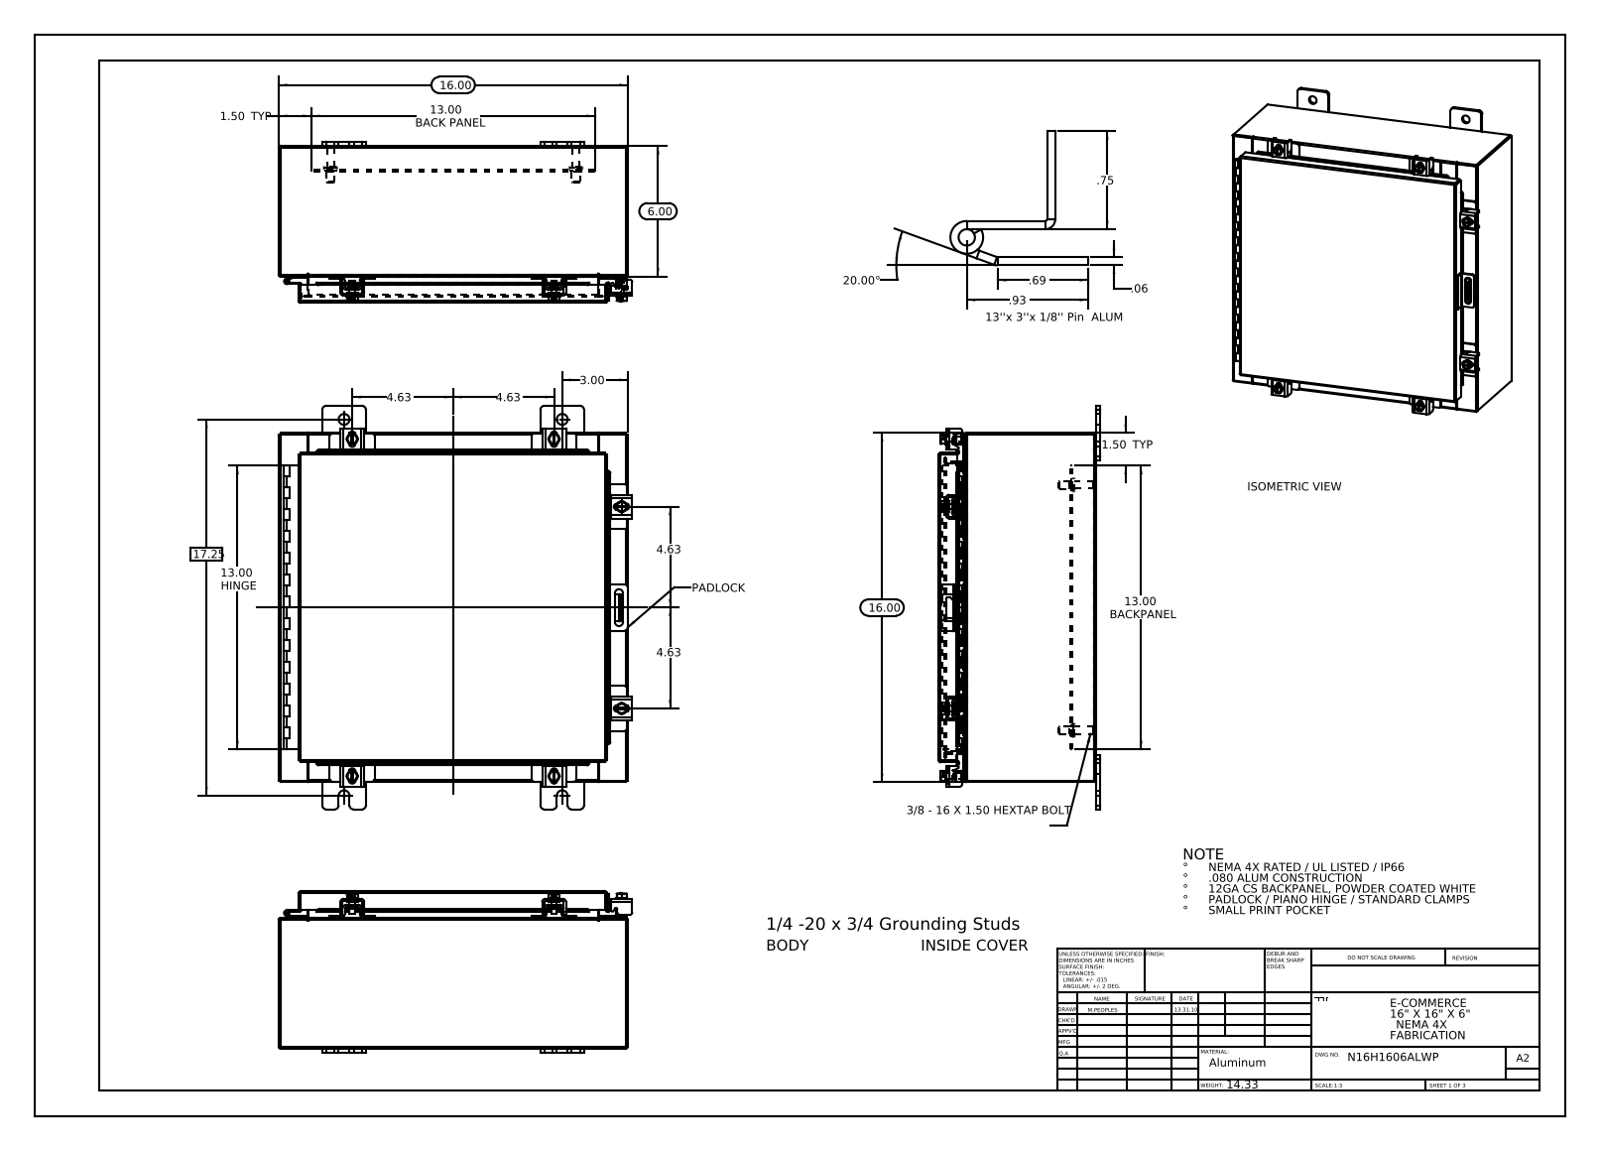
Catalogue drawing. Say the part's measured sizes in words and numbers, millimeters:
The part is named "N16H1606ALWP Backpanel; N16H1606ALWP; N16H1606ALWP 22104005_DEFAULT; N16H1606ALWP Mounting Studs (+8 more)". Its 3-D file was written by "SolidWorks 2013 (CONFIG_CONTROL_DESIGN)". It is 47 solids with 1501 faces: 800 planar, 605 cylindrical and 96 other. Overall it measures 469.9 by 411.8 by 187.7 millimeters. Its volume is 1 675 000 cubic millimeters and its surface area 1 672 000 square millimeters. Round holes: 8 of diameter 12.7, 6 of diameter 5.4, 6 of diameter 6.6, 2 of diameter 3.2, 1 of diameter 3.2. Round bosses or shafts: 7 of diameter 6.4, 6 of diameter 12.7, 6 of diameter 10.1, 4 of diameter 15.9, 4 of diameter 9.5, 4 of diameter 8.4. Partial cylindrical surfaces (rounded edges, fillets, slot ends): 30 of radius 1.5, 24 of radius 4.8, 23 of radius 0.3, 21 of radius 2.2, 12 of radius 3, 12 of radius 3.6, 10 of radius 3.2, 9 of radius 1.3. The main face-to-face distances are 1.9, 181, 404.5, 182.9, 179.1, 402.6, 406.4, 25.4, 27.3, 153.7. The hole center spacings are 340.1, 265.8, 427.5, 47.2, 59.1, 59.1, 59.1, 77.9.
